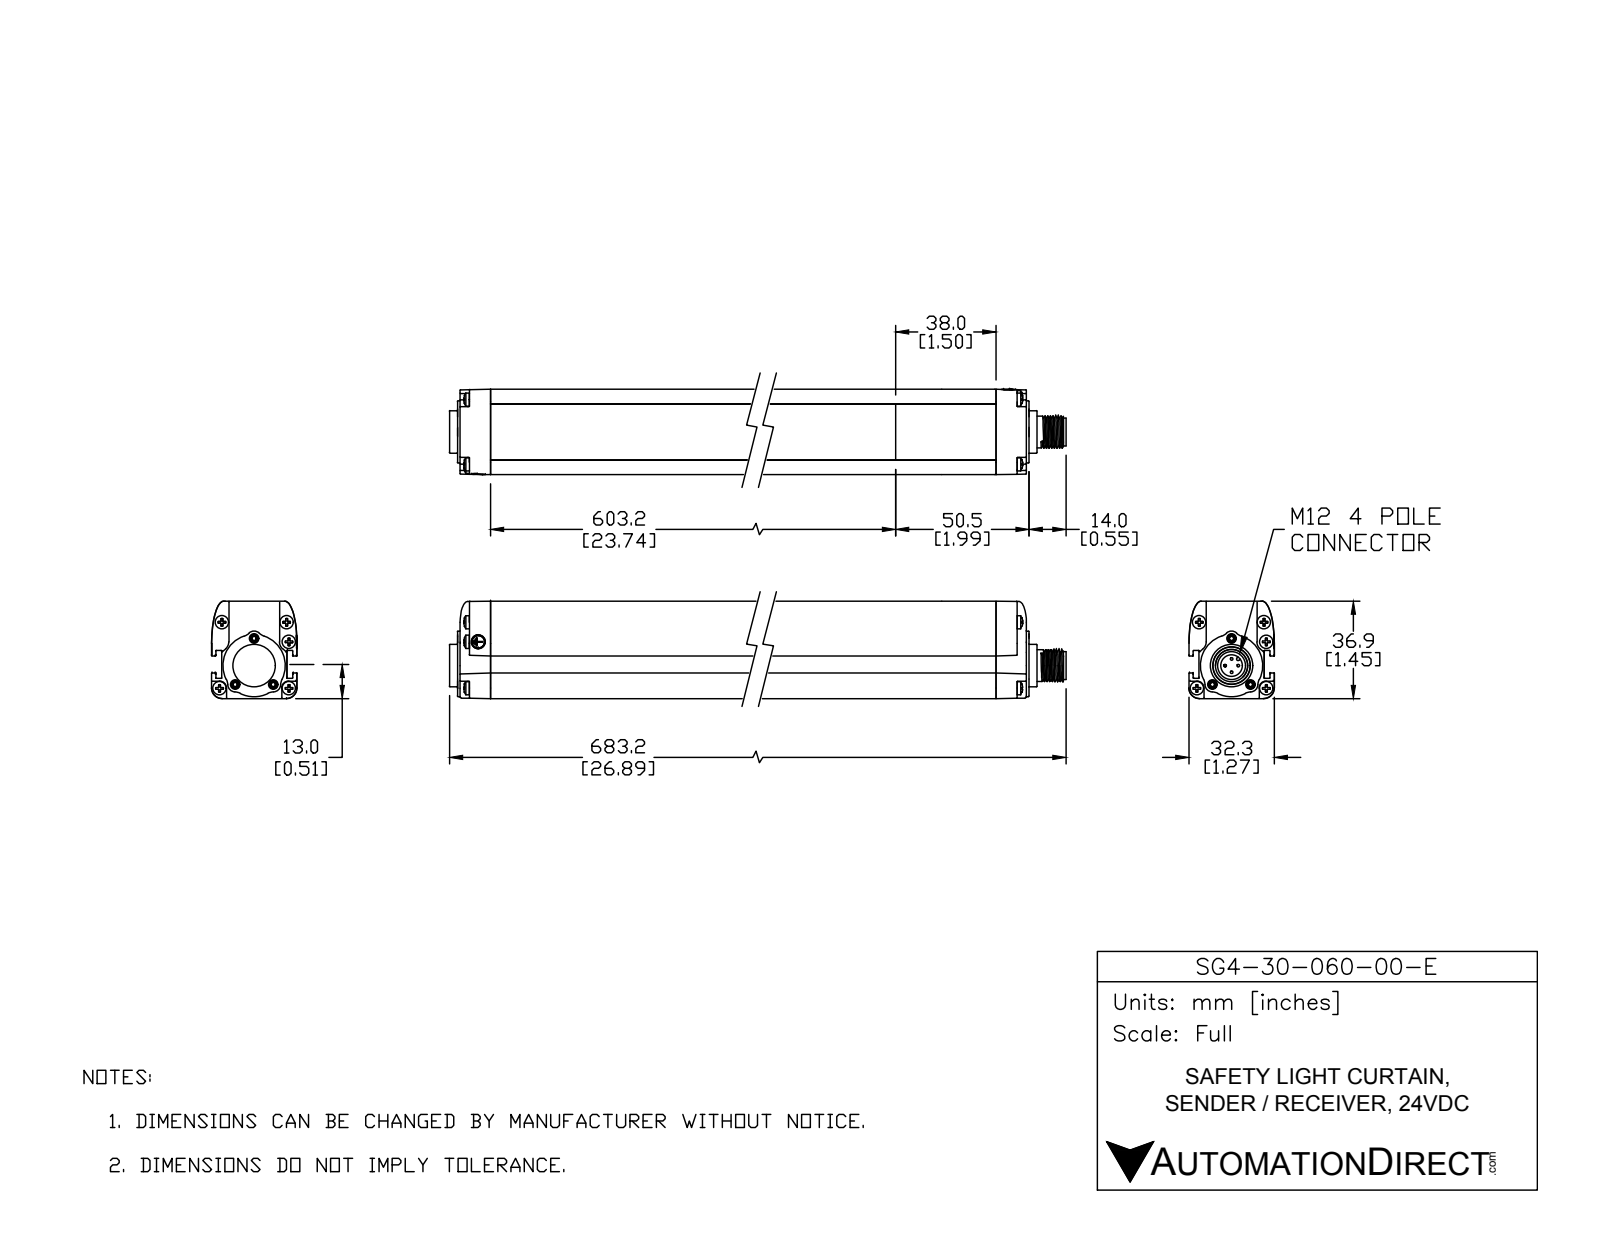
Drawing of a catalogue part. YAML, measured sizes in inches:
part_name: "SG4-30-060-OO-E"
step_written_by: "SolidWorks 2017 (AUTOMOTIVE_DESIGN)"
units: inches
bodies: {solids: 29, faces: 1674, planar: 410, cylindrical: 591, other: 673}
overall_size: [26.895, 2.48, 2.055]
volume: 42.79
surface_area: 272.3
round_holes:
  - {diameter: 0.106, count: 6}
  - {diameter: 0.209, count: 6}
  - {diameter: 0.081, count: 4}
  - {diameter: 0.165, count: 4}
  - {diameter: 0.26, count: 4}
  - {diameter: 0.059, count: 3}
  - {diameter: 0.142, count: 3}
  - {diameter: 0.323, count: 1}
  - {diameter: 0.376, count: 1}
  - {diameter: 0.433, count: 1}
  - {diameter: 0.563, count: 1}
round_bosses_or_shafts:
  - {diameter: 0.197, count: 10}
  - {diameter: 0.394, count: 4}
  - {diameter: 0.039, count: 4}
  - {diameter: 0.185, count: 2}
  - {diameter: 0.63, count: 1}
  - {diameter: 0.55, count: 1}
  - {diameter: 0.472, count: 1}
  - {diameter: 0.413, count: 1}
partial_cylinders:
  - {radius: 0.008, count: 148}
  - {radius: 0.004, count: 120}
  - {radius: 0.006, count: 18}
  - {radius: 0.106, count: 18}
  - {radius: 0.118, count: 8}
  - {radius: 0.197, count: 7}
  - {radius: 0.11, count: 3}
  - {radius: 0.016, count: 2}
face_to_face_distances: [0.079, 1.272, 1.429, 0.15, 1.122, 1.35, 0.157, 0.972, 0.118, 0.333]
hole_center_spacings: [0.569, 23.667, 0.402, 0.24, 0.293, 0.52, 0.541, 0.619]
